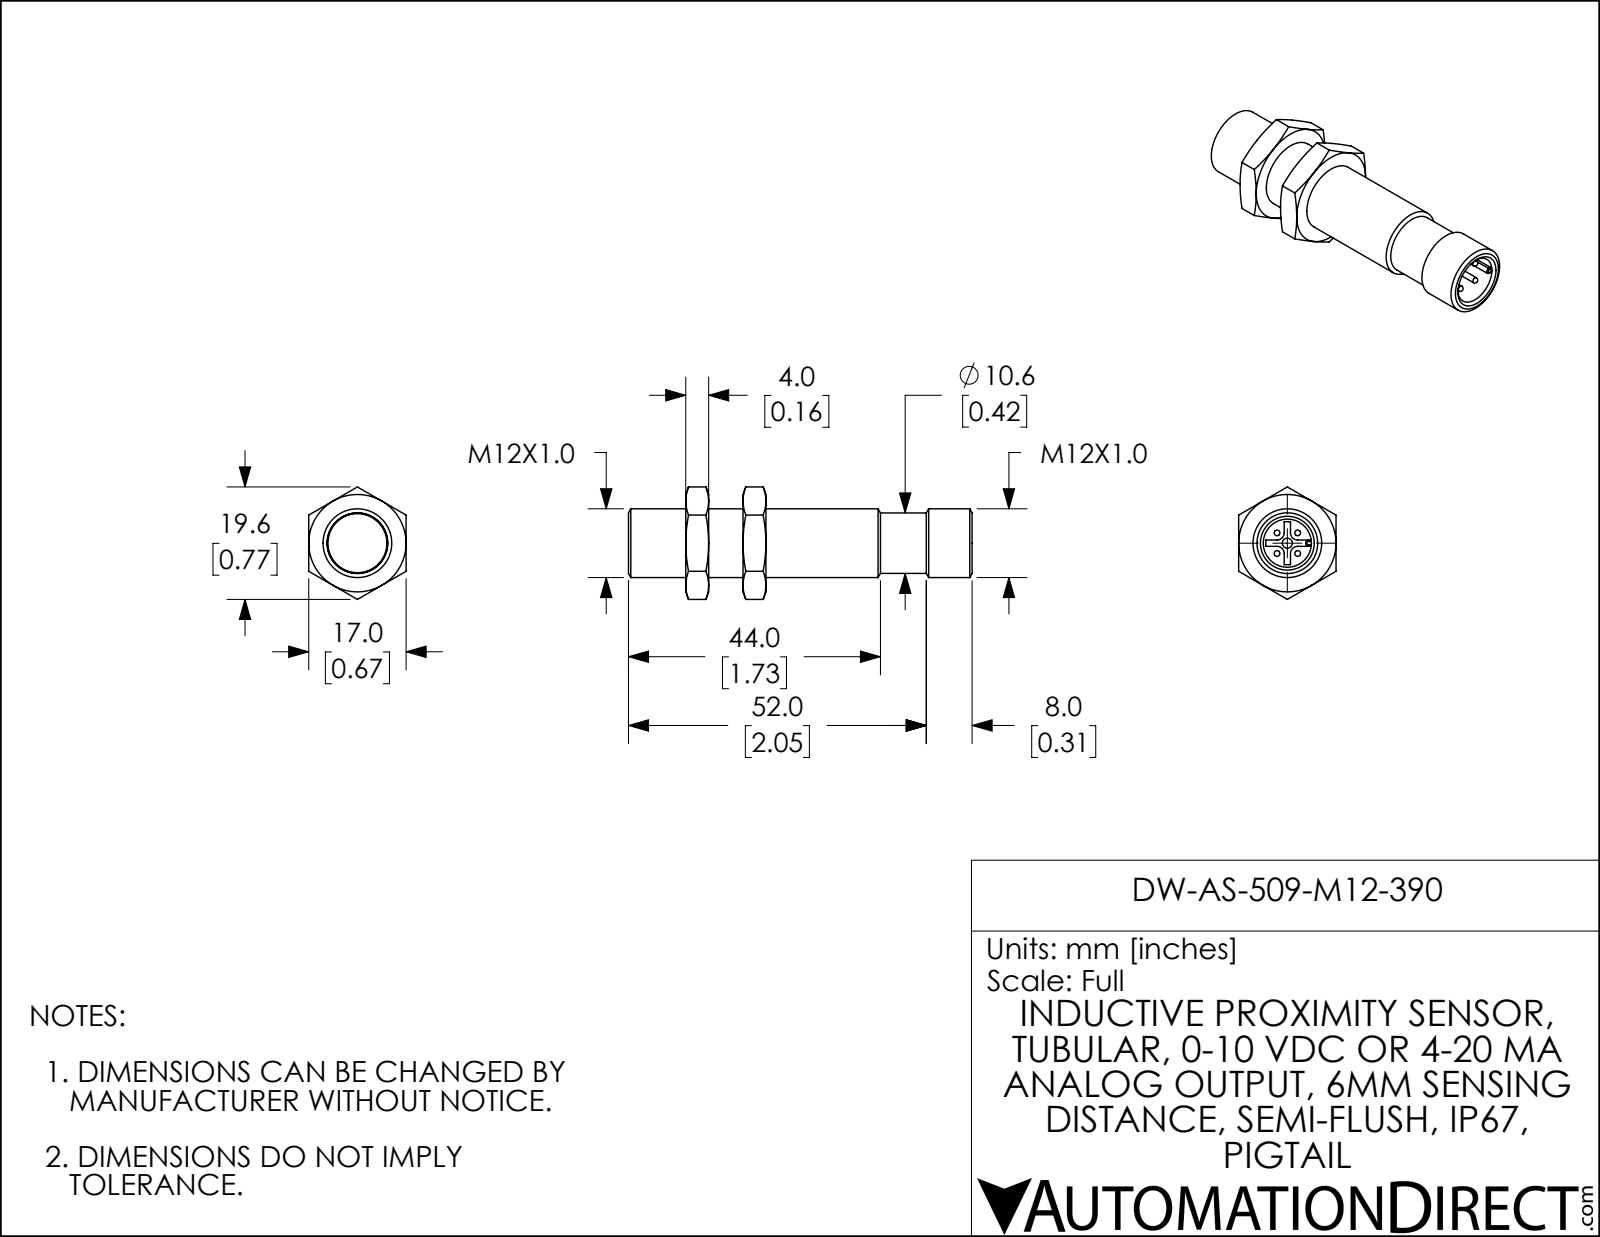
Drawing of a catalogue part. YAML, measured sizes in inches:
part_name: "DW-AS-509-M12-390"
step_written_by: "SolidWorks 2018 (AUTOMOTIVE_DESIGN)"
units: inches
bodies: {solids: 1, faces: 93, planar: 38, cylindrical: 20, other: 35}
overall_size: [2.362, 0.773, 0.669]
volume: 0.436
surface_area: 5.444
round_holes:
  - {diameter: 0.069, count: 1}
  - {diameter: 0.331, count: 1}
  - {diameter: 0.415, count: 1}
round_bosses_or_shafts:
  - {diameter: 0.039, count: 4}
  - {diameter: 0.472, count: 1}
  - {diameter: 0.415, count: 1}
  - {diameter: 0.406, count: 1}
partial_cylinders:
  - {radius: 0.049, count: 4}
  - {radius: 0.008, count: 2}
  - {radius: 0.02, count: 1}
face_to_face_distances: [0.394, 0.157, 0.669, 0.551, 0.236, 0.787, 0.945, 2.008, 1.614, 1.457]
